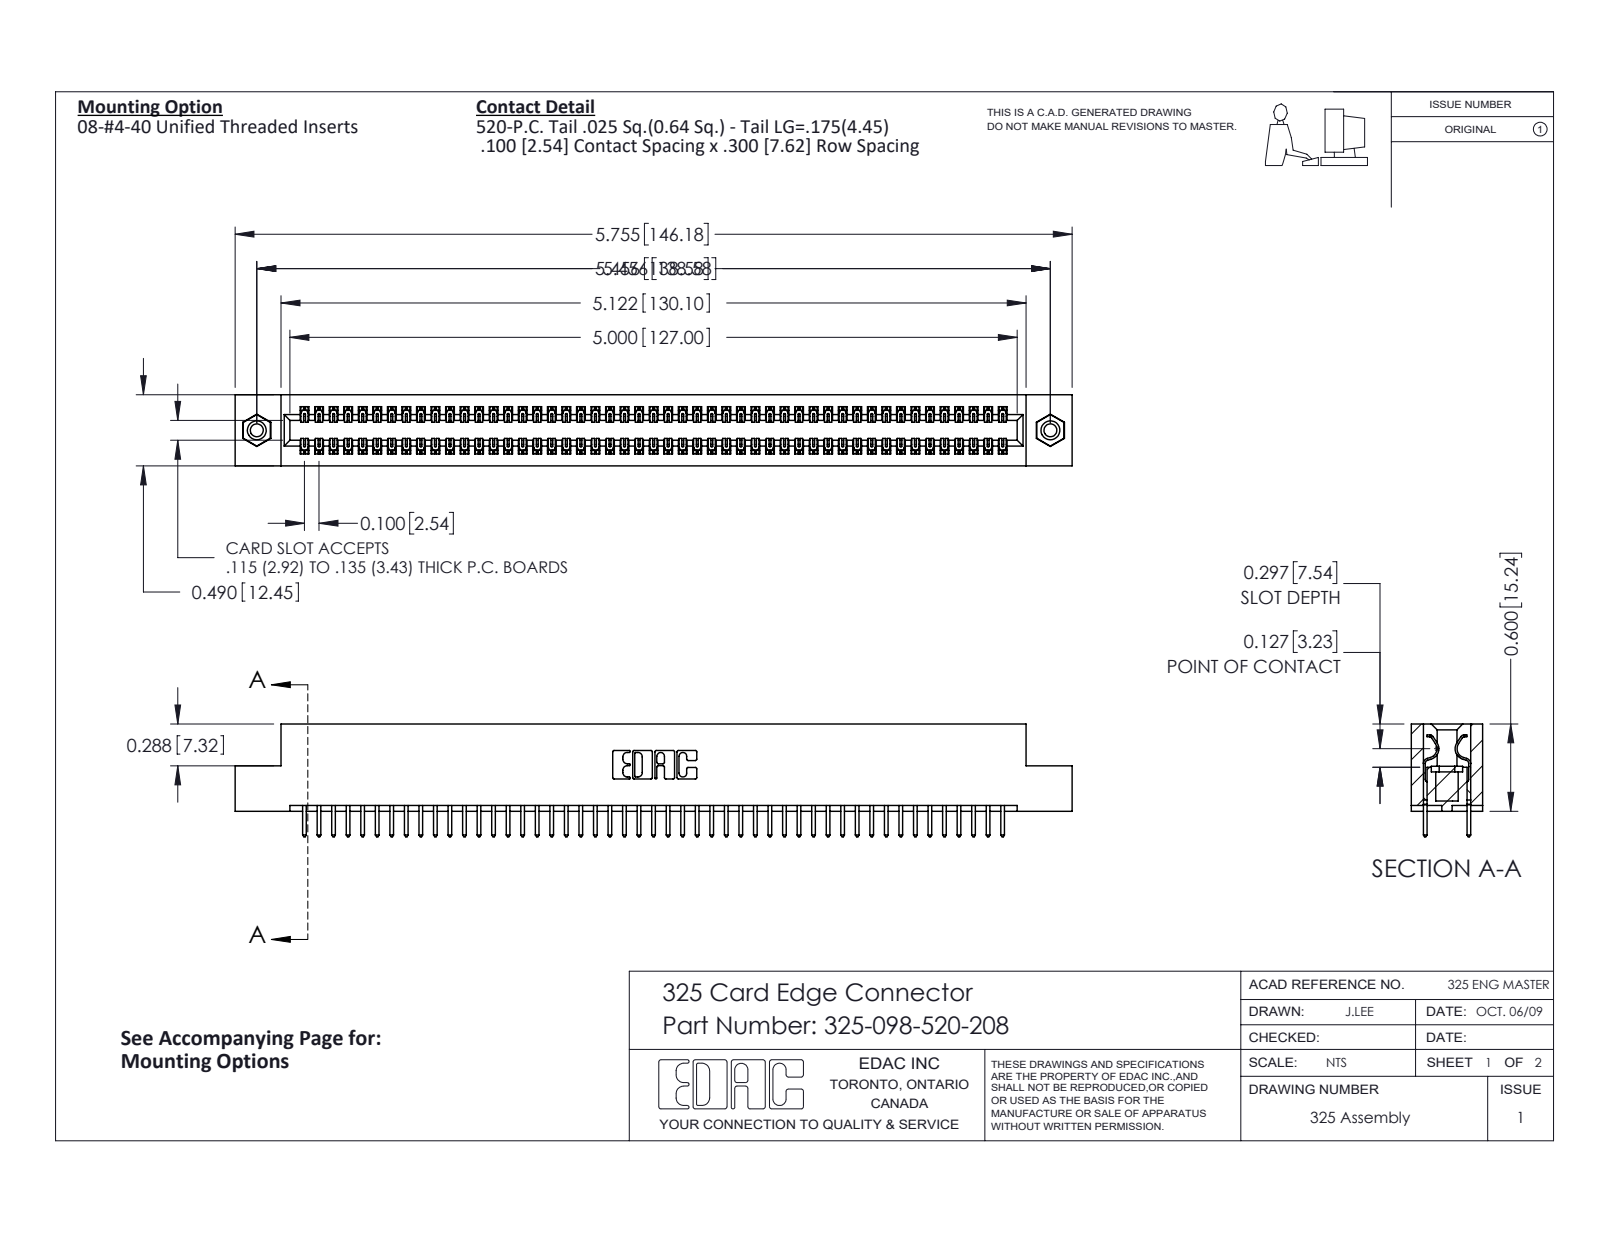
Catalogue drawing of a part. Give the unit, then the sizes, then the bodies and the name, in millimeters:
Units: millimetres
Overall size (bounding box): 146.2 × 19.7 × 12.4
Round holes (diameter × count): ⌀2.3 ×2, ⌀3.2 ×2, ⌀4.1 ×2
Round bosses / shafts (diameter × count): ⌀3.9 ×2
Partial cylindrical surfaces — rounded edges, fillets, slot ends (radius × count): R0.2 ×147, R0.3 ×98, R0.3 ×22, R0.2 ×6, R0.8 ×6, R0.7 ×3, R0.4 ×2, R0.6 ×2
Main face-to-face distances: 2.1, 10.3, 7.6, 12.4, 2.7, 9.7, 0.6, 8.3, 7, 14.2
Hole centre spacings: 138.6
Volume: 18 910 mm³ · Surface area: 22 870 mm²
Bodies: 101 solids, 5270 faces (3630 planar, 1624 cylindrical, 16 other)
Part name (STEP PRODUCT): 345-250-001_345-250-003-102; 325 Part_TI; 325-292-001_325-293-120; 325-098-520-208
STEP written by: SolidWorks 2016 (CONFIG_CONTROL_DESIGN)
